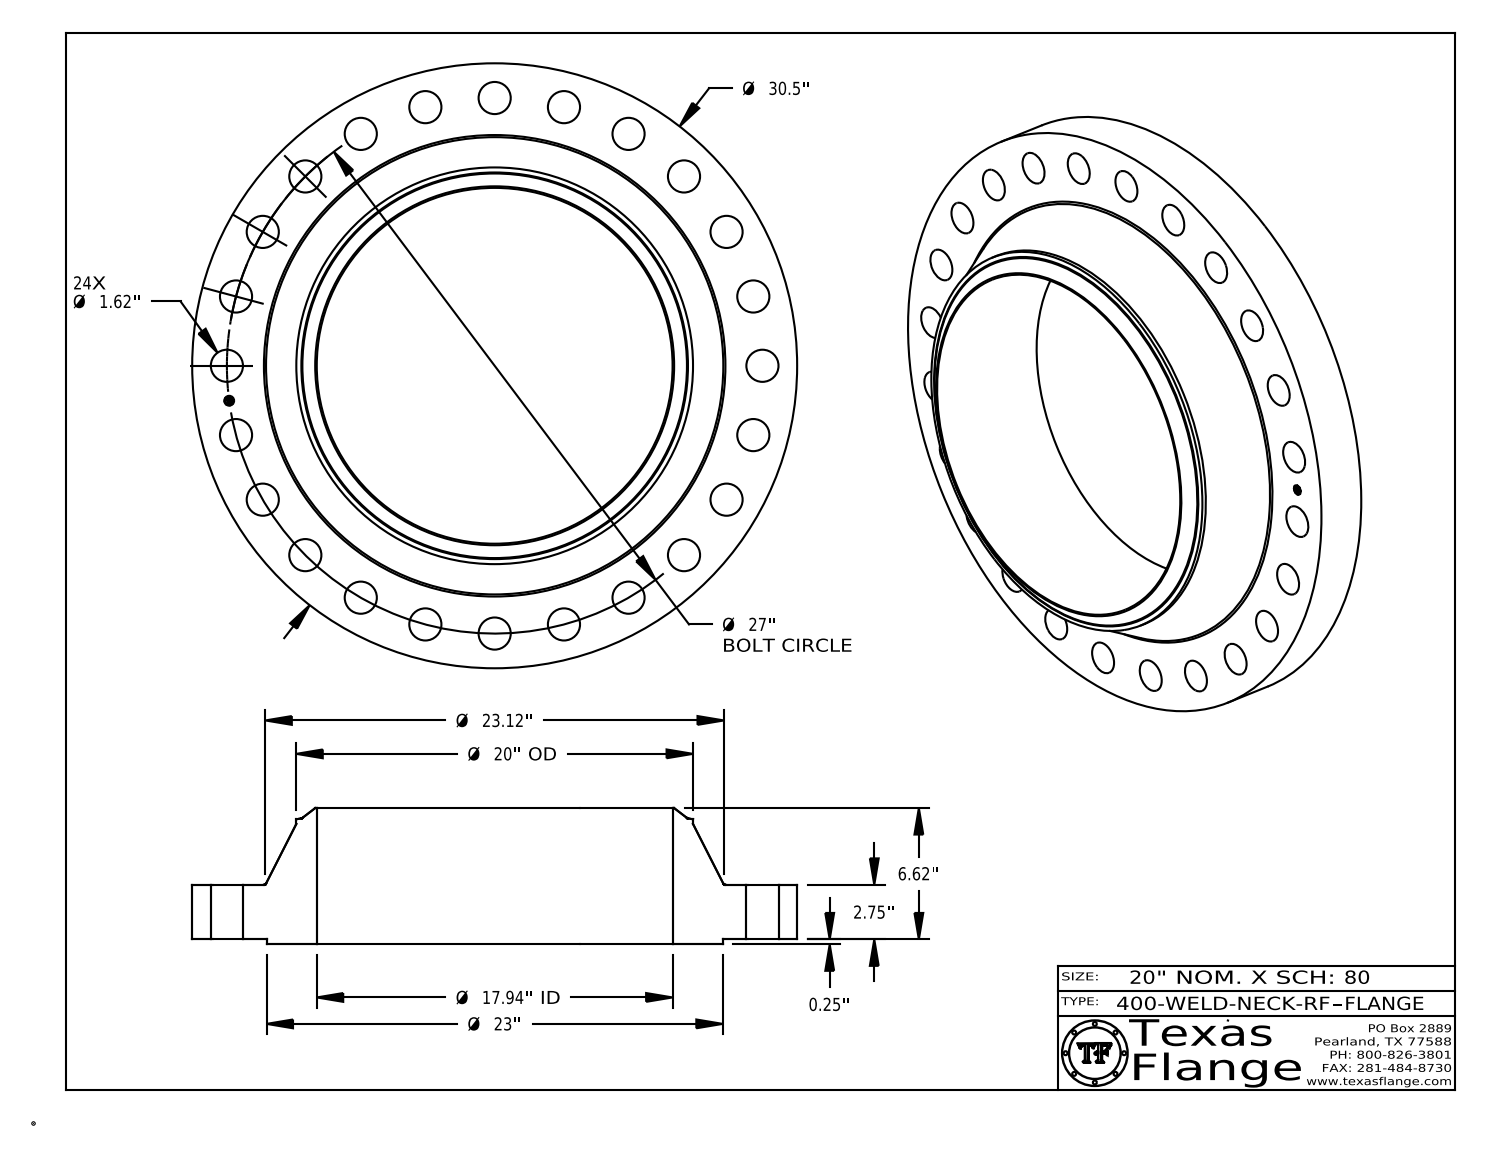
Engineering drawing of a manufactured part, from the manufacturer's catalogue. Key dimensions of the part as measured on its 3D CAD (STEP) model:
Part name (STEP PRODUCT): 400-WELD-NECK-RF
STEP written by: CATIA V5 STEP AP214 (AUTOMOTIVE_DESIGN)
Units: inches
Bodies: 1 solid, 455 faces (369 planar, 76 cylindrical, 10 other)
Overall size (bounding box): 30.5 × 30.5 × 6.87
Volume: 1 595 in³ · Surface area: 2 013 in²
Round holes (diameter × count): ⌀1.62 ×24, ⌀0.495 ×1, ⌀17.938 ×1
Round bosses / shafts (diameter × count): ⌀0.03 ×8, ⌀30.5 ×1, ⌀23 ×1, ⌀20 ×1, ⌀0.39 ×1
Main face-to-face distances: 2.75, 0.25, 3, 6.87, 6.62, 3.87, 2.985, 2.735, 0.015, 3.885
Hole centre spacings: 13.5, 3.524, 6.988, 10.333, 16.437, 24.945, 26.769, 21.421
